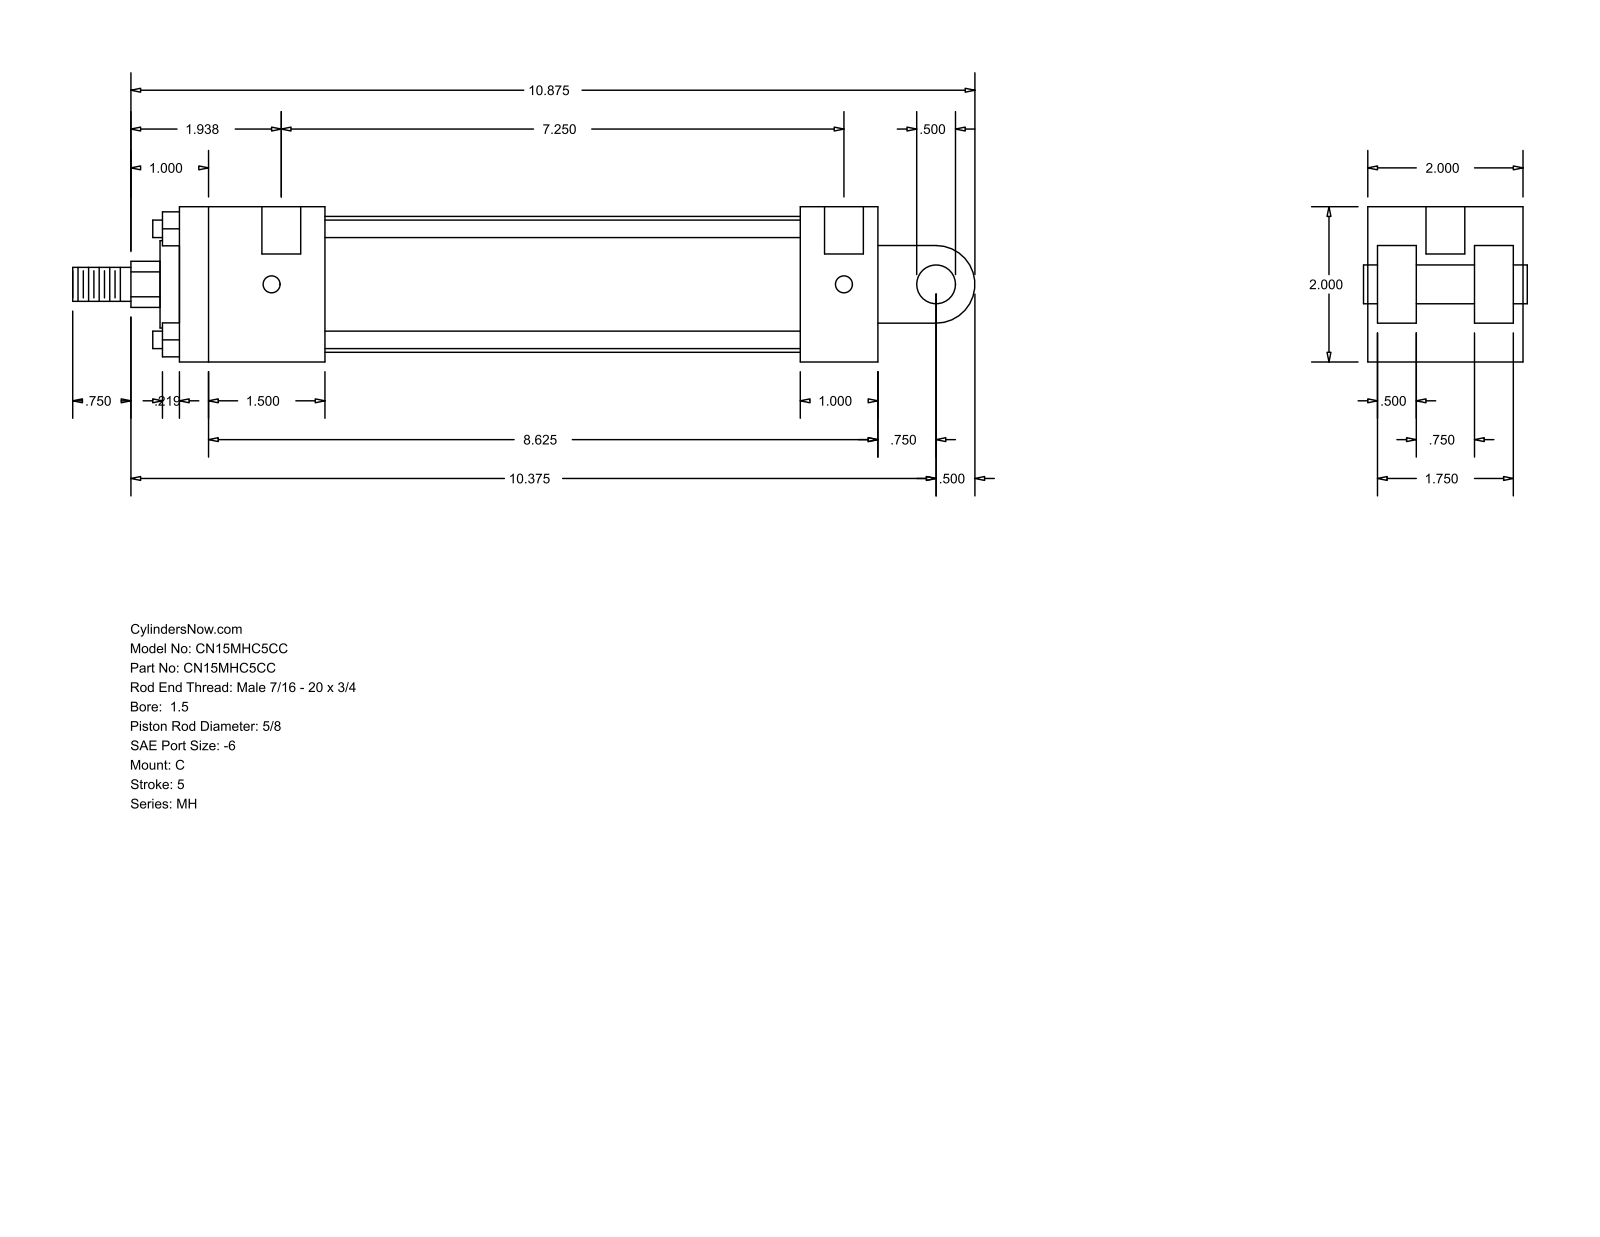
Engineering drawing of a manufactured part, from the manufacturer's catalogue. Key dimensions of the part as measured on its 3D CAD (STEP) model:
Part name (STEP PRODUCT): MH_C__0150_0.625
STEP written by: GSSL Pune (CONFIG_CONTROL_DESIGN)
Units: millimetres
Bodies: 0 solids, 99 faces (70 planar, 29 cylindrical, 0 other)
Overall size (bounding box): 295.27 × 50.8 × 50.8
Round holes (diameter × count): ⌀5.56 ×4, ⌀12.7 ×2
Round bosses / shafts (diameter × count): ⌀5.71 ×4, ⌀44.45 ×1, ⌀28.57 ×1, ⌀15.88 ×1, ⌀12.7 ×1, ⌀11.11 ×1
Partial cylindrical surfaces — rounded edges, fillets, slot ends (radius × count): R7.54 ×1, R12.7 ×1
Main face-to-face distances: 50.8, 12.7, 228.59, 25.4, 34.93, 3.17, 15.87, 47.63, 31.76, 38.1
Hole centre spacings: 187.32, 3.17, 184.15
